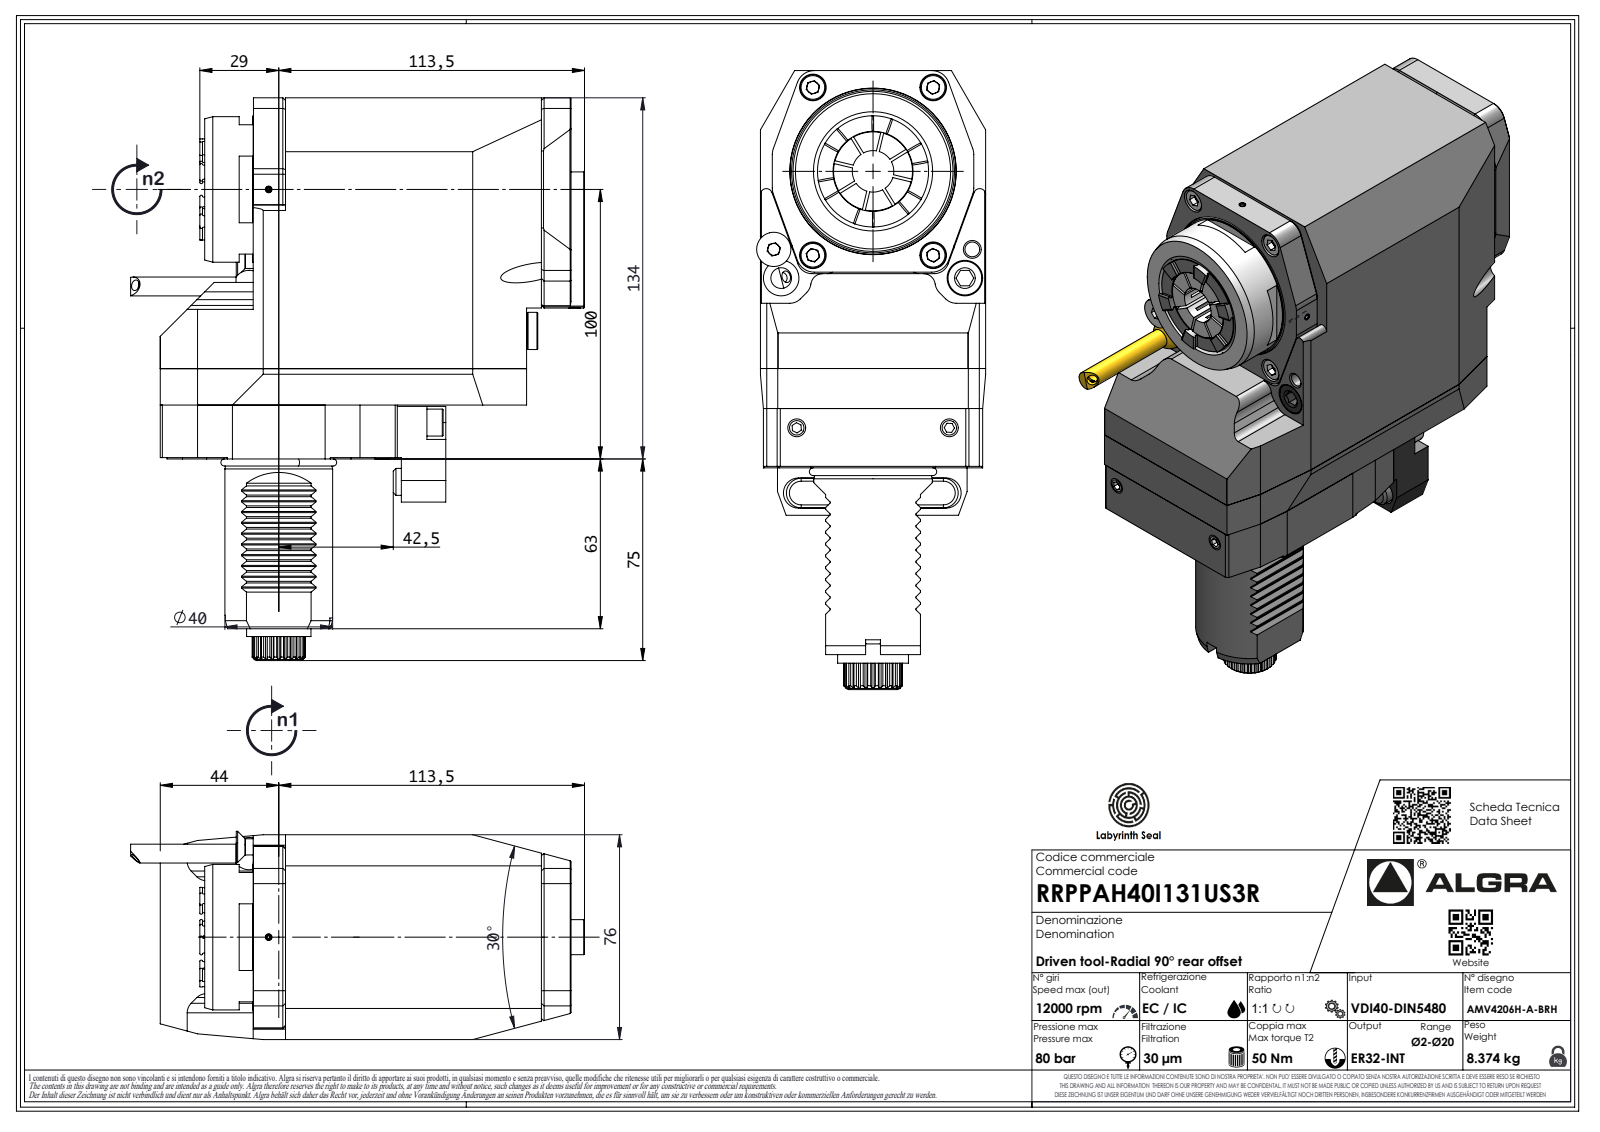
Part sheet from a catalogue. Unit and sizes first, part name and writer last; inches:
Units: inches
Overall size (bounding box): 8.22 × 6.634 × 2.992
Round holes (diameter × count): ⌀0.551 ×4, ⌀0.197 ×2, ⌀0.268 ×2, ⌀0.081 ×1, ⌀0.083 ×1, ⌀0.157 ×1, ⌀0.236 ×1, ⌀1.197 ×1
Round bosses / shafts (diameter × count): ⌀2.126 ×1, ⌀1.575 ×1, ⌀1.524 ×1, ⌀0.941 ×1, ⌀0.689 ×1, ⌀0.276 ×1, ⌀0.251 ×1, ⌀0.067 ×1
Partial cylindrical surfaces — rounded edges, fillets, slot ends (radius × count): R0.012 ×20, R0.236 ×10, R0.197 ×8, R0.013 ×7, R0.02 ×7, R0.146 ×7, R0.079 ×3, R0.02 ×2
Main face-to-face distances: 2.992, 0.65, 5.354, 4.488, 1.831, 5.276, 0.787, 2.815, 0.709, 3.524
Hole centre spacings: 1.648, 1.218, 2.126, 2.199, 2.52, 3.297, 0.665
Volume: 77.93 in³ · Surface area: 154.1 in²
Bodies: 2 solids, 872 faces (555 planar, 159 cylindrical, 158 other)
Part name (STEP PRODUCT): RRPPAH40I131US3R
STEP written by: SolidWorks 2023 (AUTOMOTIVE_DESIGN)
